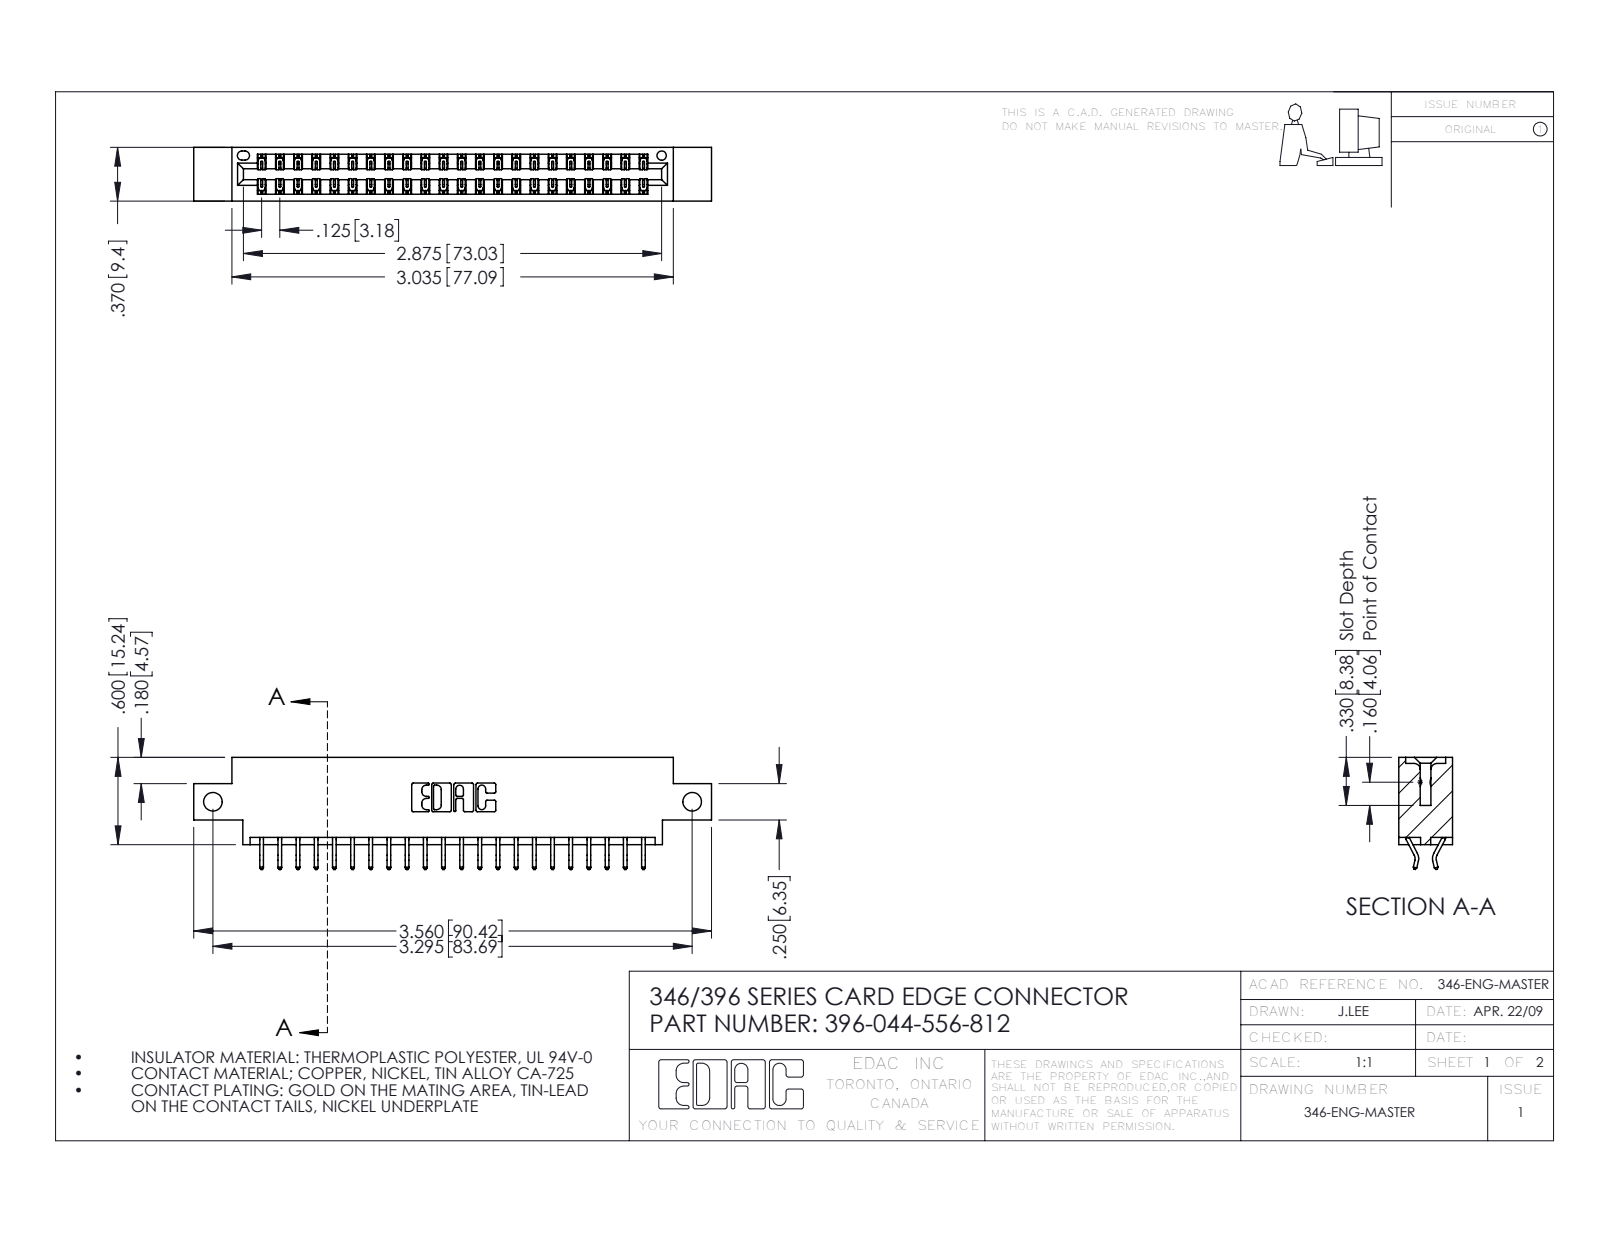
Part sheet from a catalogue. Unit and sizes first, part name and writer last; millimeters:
Units: millimetres
Overall size (bounding box): 90.4 × 19.6 × 9.4
Round holes (diameter × count): ⌀3.3 ×2, ⌀1.6 ×1
Partial cylindrical surfaces — rounded edges, fillets, slot ends (radius × count): R0.2 ×66, R0.3 ×22, R0.2 ×6, R0.8 ×6, R0.7 ×3, R0.3 ×2, R0.4 ×2, R0.6 ×2
Main face-to-face distances: 1.2, 8.2, 9.4, 6.4, 0.6, 1.8, 7.6, 7, 3.8, 5.6
Hole centre spacings: 83.7
Volume: 8 420 mm³ · Surface area: 11 260 mm²
Bodies: 45 solids, 2678 faces (1796 planar, 882 cylindrical, 0 other)
Part name (STEP PRODUCT): 346 Part_0.170 Offset - Side Mount; 345-292-001_556 Tail; 396-044-556-812
STEP written by: SolidWorks 2016 (CONFIG_CONTROL_DESIGN)
